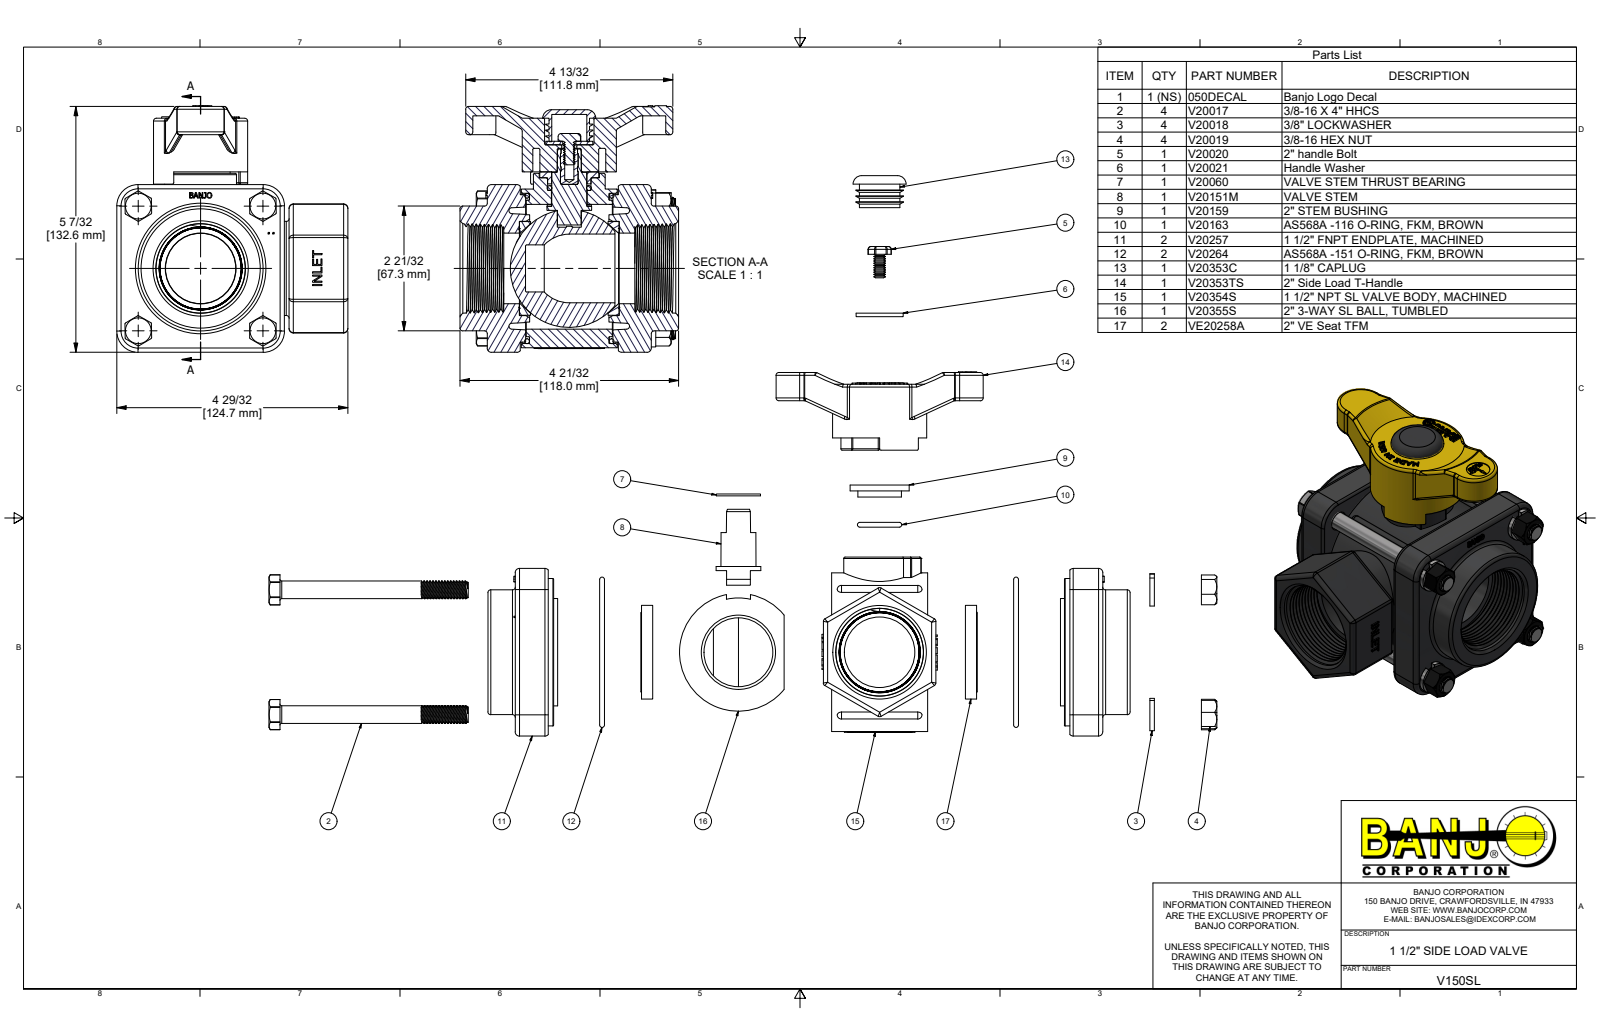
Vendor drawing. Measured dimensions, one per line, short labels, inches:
name: V150SL; 050DECAL; V20017; V20018 (+8 more)
written by: Autodesk Inventor 2022 (AUTOMOTIVE_DESIGN)
unit: in
bodies: 30 solids, 3011 faces (1453 planar, 540 cylindrical, 1018 other)
size: 5.235 × 4.91 × 4.645
volume: 39.14 in³; area: 318.1 in²
holes: 4× ⌀0.307, 4× ⌀0.385, 4× ⌀0.42, 2× ⌀1.46, 2× ⌀1.5, 1× ⌀0.172, 1× ⌀0.196, 1× ⌀0.227, 1× ⌀0.244, 1× ⌀0.281, 1× ⌀0.32, 1× ⌀0.321
bosses: 60× ⌀0.324, 4× ⌀0.687, 4× ⌀0.375, 2× ⌀2, 1× ⌀3.37, 1× ⌀3.13, 1× ⌀2.9, 1× ⌀2.65
rounds: 46× R0.06, 32× R0.09, 26× R0.03, 8× R0.075, 8× R0.162, 4× R0.062, 4× R0.125, 4× R0.32
face distances: 0.7, 2.785, 0.35, 3.56, 3.485, 0.683, 2.802, 0.017, 2.102, 0.815
hole spacings: 1.872, 2.648, 3.745, 0.5, 0.716, 0.783, 1.825, 2.285
